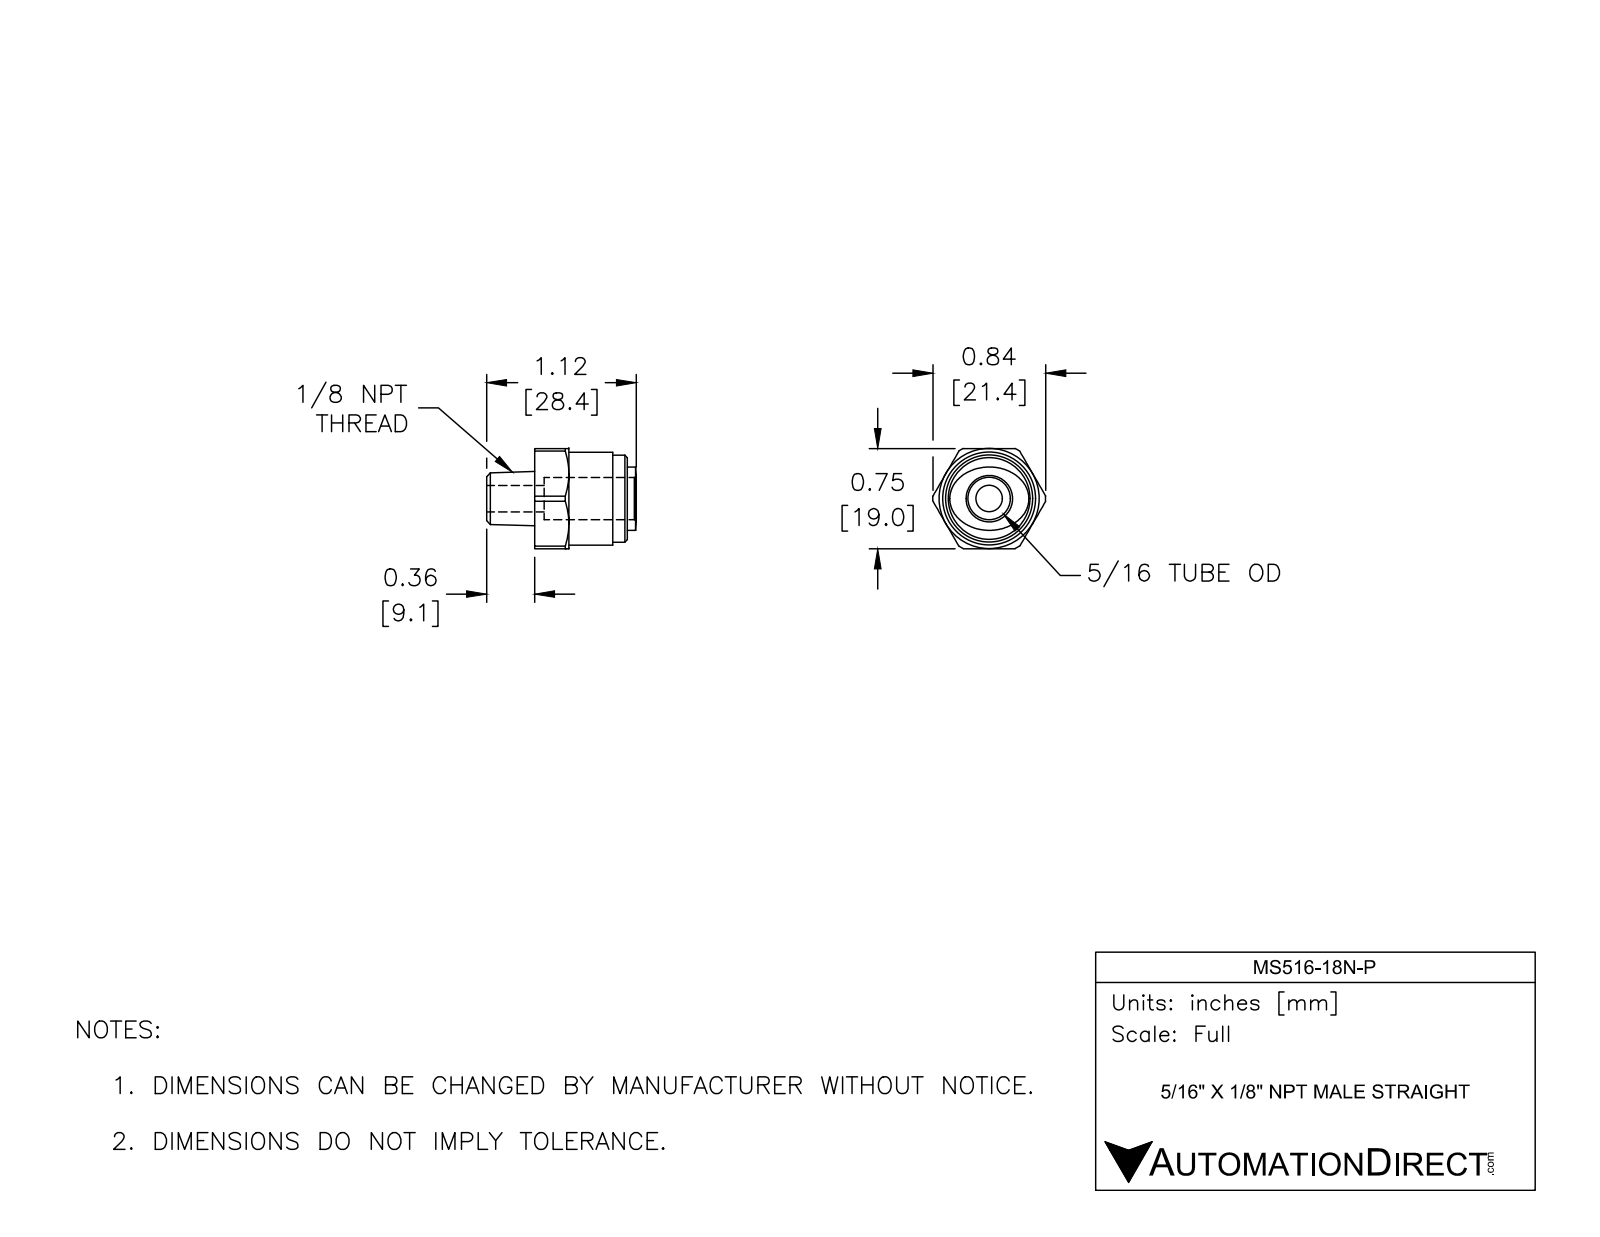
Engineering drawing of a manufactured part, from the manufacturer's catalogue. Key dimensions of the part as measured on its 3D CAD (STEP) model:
Part name (STEP PRODUCT): MS516-18N-P
STEP written by: SolidWorks 2017 (AUTOMOTIVE_DESIGN)
Units: inches
Bodies: 1 solid, 44 faces (12 planar, 14 cylindrical, 18 other)
Overall size (bounding box): 1.118 × 0.843 × 0.748
Volume: 0.273 in³ · Surface area: 3.903 in²
Round holes (diameter × count): ⌀0.197 ×1, ⌀0.315 ×1
Round bosses / shafts (diameter × count): ⌀0.693 ×1, ⌀0.65 ×1
Partial cylindrical surfaces — rounded edges, fillets, slot ends (radius × count): R0.421 ×1
Main face-to-face distances: 0.748, 0.693, 0.256, 0.437, 0.358, 0.614, 1.051, 0.429, 0.071, 0.185
